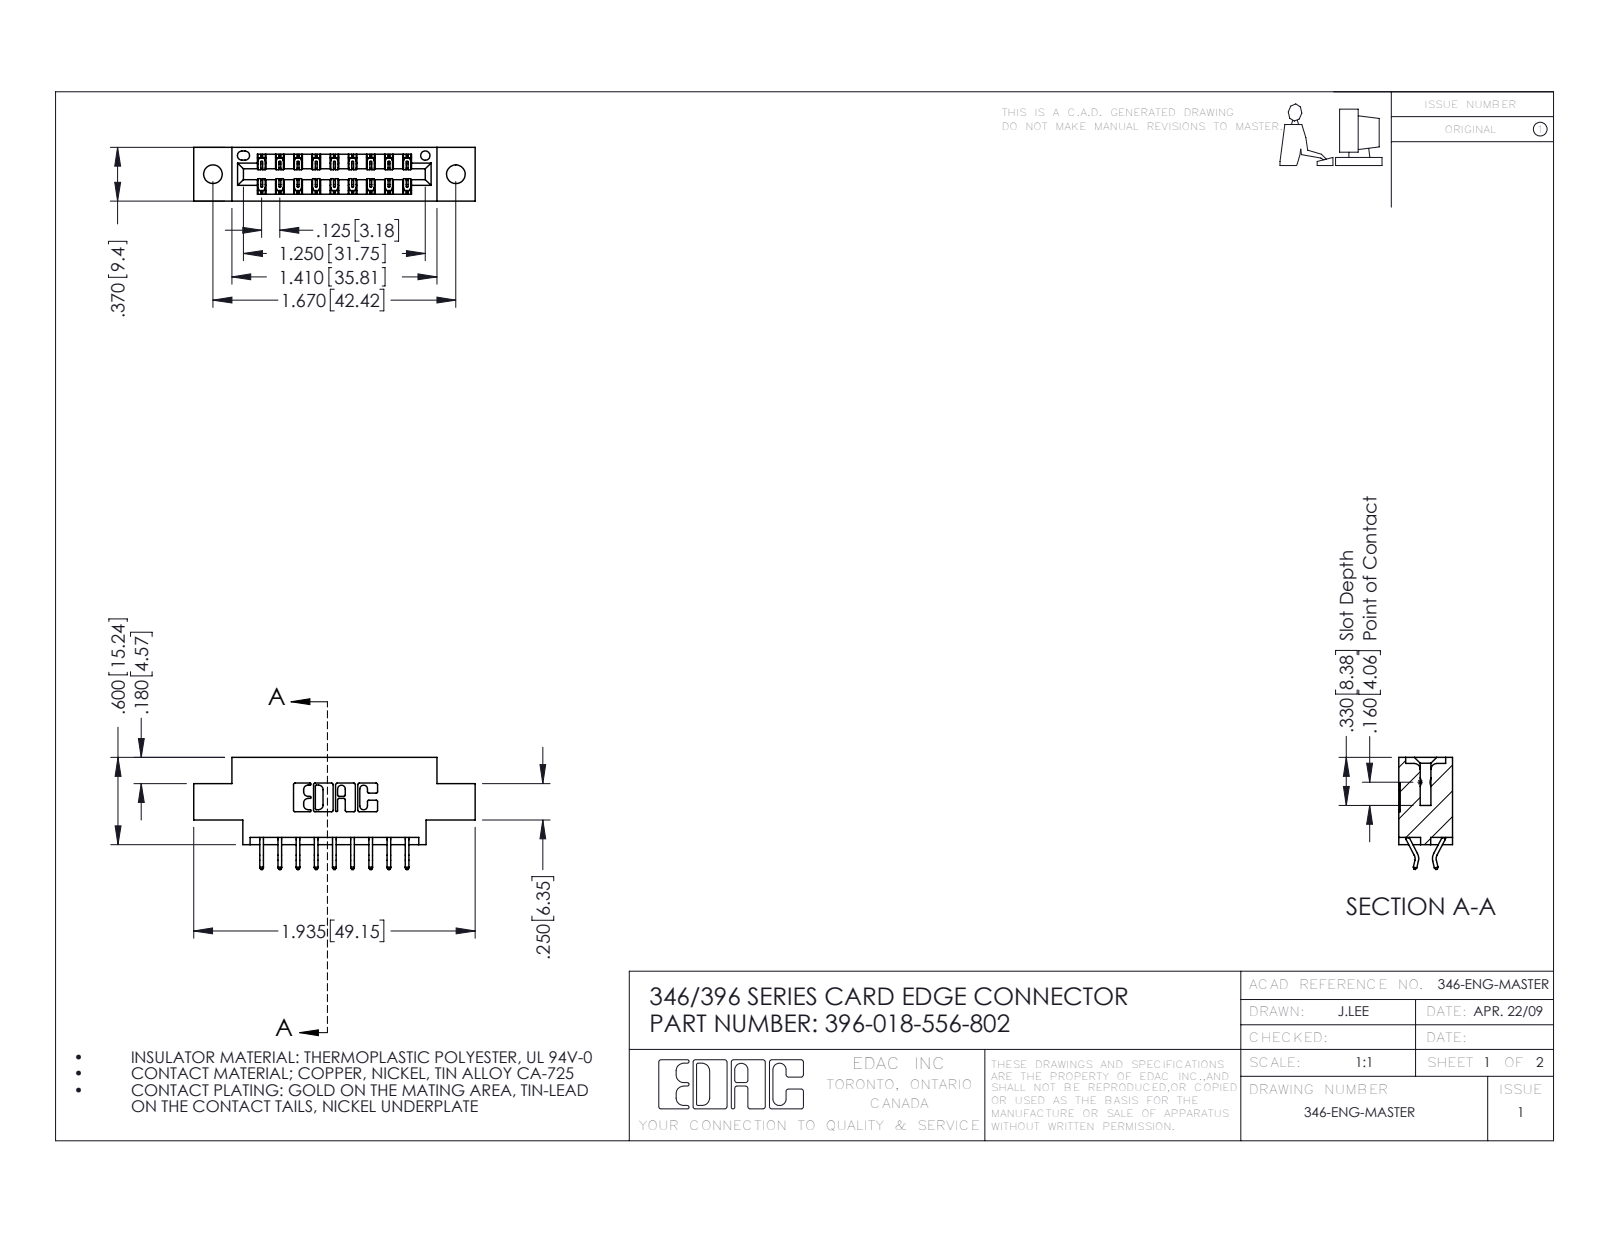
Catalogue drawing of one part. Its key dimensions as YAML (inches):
part_name: "345-292-001_556 Tail; 396-018-556-802; 346 Part_0.170 Offset - 0.128 Dia"
step_written_by: "SolidWorks 2016 (CONFIG_CONTROL_DESIGN)"
units: inches
bodies: {solids: 19, faces: 1170, planar: 782, cylindrical: 388, other: 0}
overall_size: [1.935, 0.77, 0.37]
volume: 0.265
surface_area: 8.287
round_holes:
  - {diameter: 0.128, count: 2}
  - {diameter: 0.064, count: 1}
partial_cylinders:
  - {radius: 0.006, count: 27}
  - {radius: 0.01, count: 22}
  - {radius: 0.007, count: 6}
  - {radius: 0.031, count: 6}
  - {radius: 0.026, count: 3}
  - {radius: 0.01, count: 2}
  - {radius: 0.014, count: 2}
  - {radius: 0.022, count: 2}
face_to_face_distances: [0.25, 0.37, 0.048, 0.322, 0.025, 0.148, 0.222, 0.1, 0.174, 0.072]
hole_center_spacings: [0.246, 1.465, 1.67]
